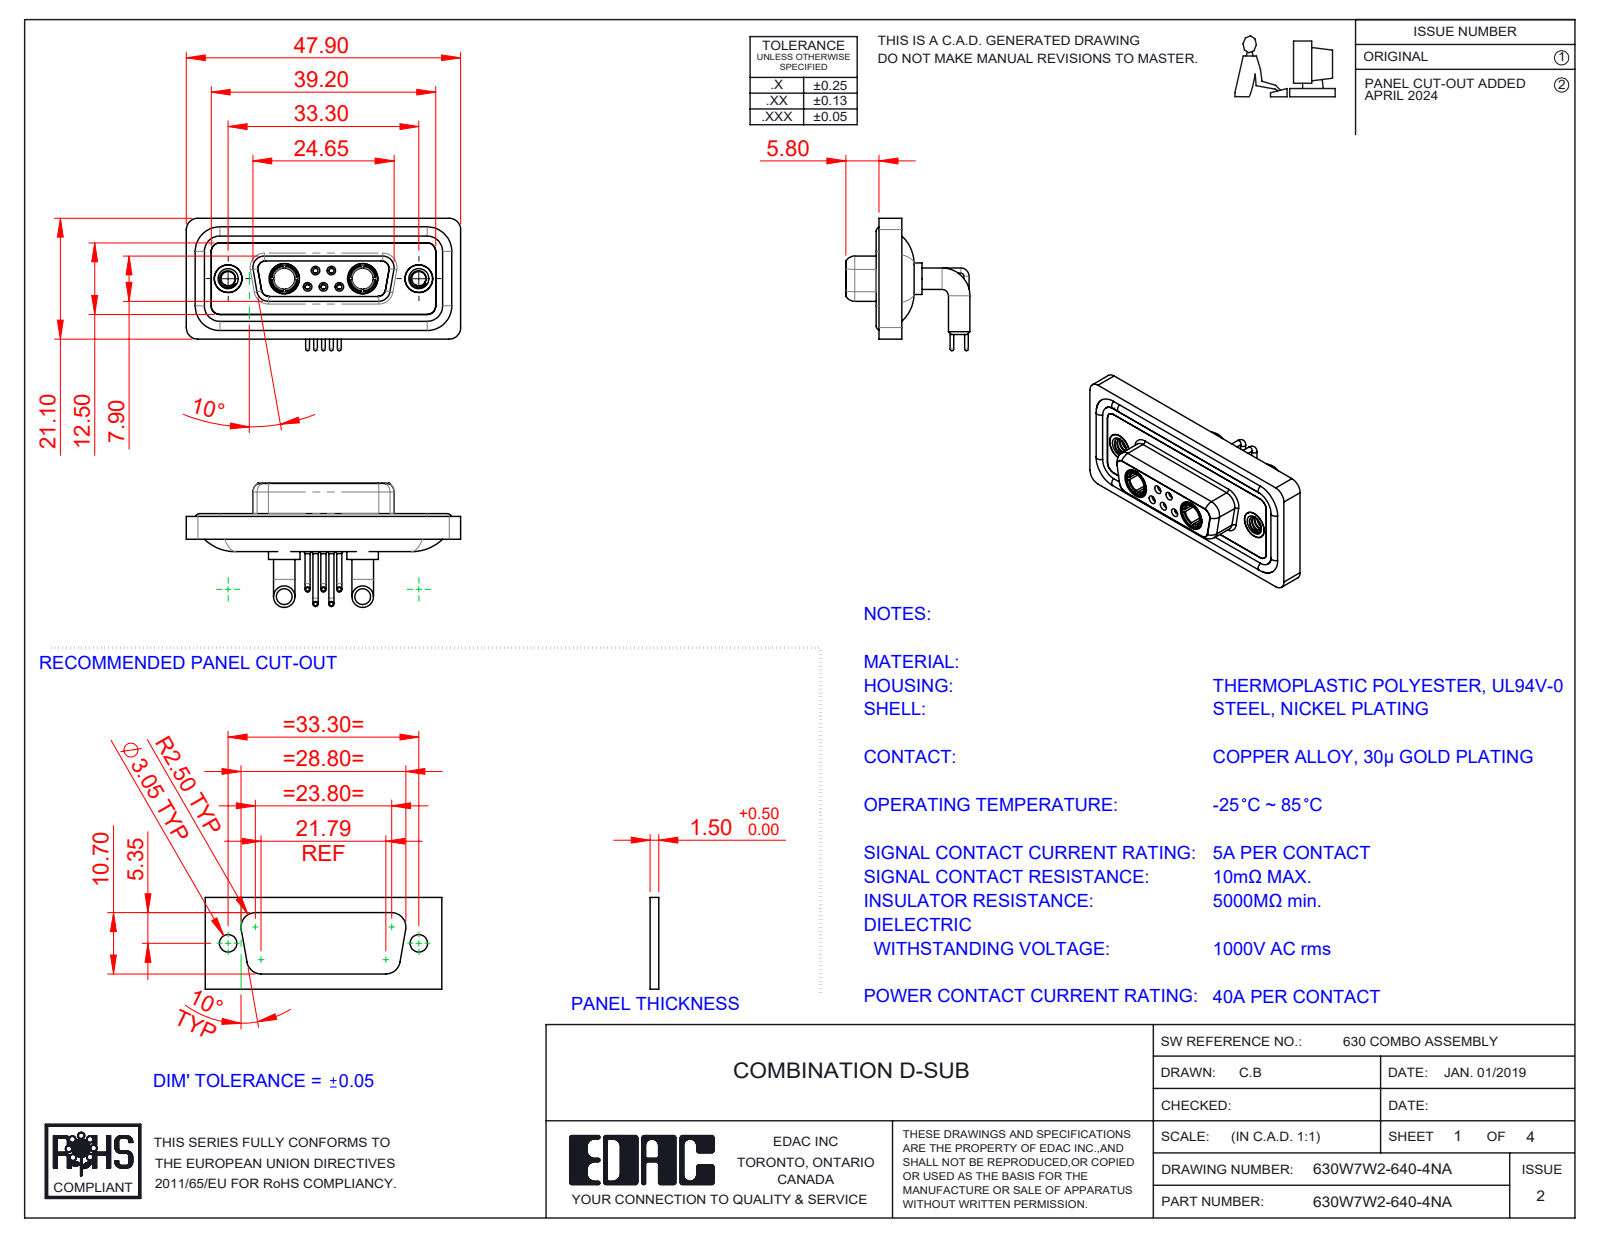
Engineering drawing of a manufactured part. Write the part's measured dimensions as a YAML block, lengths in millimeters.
part_name: "630Combo Threaded Rivet_A; 630Combo Shell Rear_15 Contacts; 630Combo Contact Row 1_50 Contacts; 630Combo Shell Front_15 Contacts (+5 more)"
step_written_by: "SolidWorks 2023 (CONFIG_CONTROL_DESIGN)"
units: millimeters
bodies: {solids: 16, faces: 801, planar: 238, cylindrical: 351, other: 212}
overall_size: [47.9, 23.12, 21.68]
volume: 6334
surface_area: 10296
round_holes:
  - {diameter: 0.9, count: 5}
  - {diameter: 1.1, count: 5}
  - {diameter: 1.5, count: 5}
  - {diameter: 2, count: 5}
  - {diameter: 4.85, count: 4}
  - {diameter: 1.6, count: 3}
  - {diameter: 1.7, count: 2}
  - {diameter: 2.5, count: 2}
  - {diameter: 3.7, count: 2}
  - {diameter: 4, count: 2}
  - {diameter: 4.05, count: 2}
  - {diameter: 5, count: 2}
round_bosses_or_shafts:
  - {diameter: 1.6, count: 6}
  - {diameter: 0.9, count: 5}
  - {diameter: 0.65, count: 5}
  - {diameter: 3.75, count: 4}
  - {diameter: 5.5, count: 2}
  - {diameter: 5.2, count: 2}
  - {diameter: 4.96, count: 2}
  - {diameter: 4.95, count: 2}
partial_cylinders:
  - {radius: 2, count: 20}
  - {radius: 1.5, count: 18}
  - {radius: 1.35, count: 12}
  - {radius: 1.6, count: 8}
  - {radius: 0.25, count: 4}
  - {radius: 0.5, count: 4}
  - {radius: 0.6, count: 4}
  - {radius: 0.65, count: 4}
face_to_face_distances: [0.4, 1.8, 1.1, 1.6, 2.9, 2.5, 3.1, 3.7, 4.1, 1.5]
hole_center_spacings: [3.16, 2.77, 9.8, 23.5, 4.31, 4.33, 5.03, 5.04]
